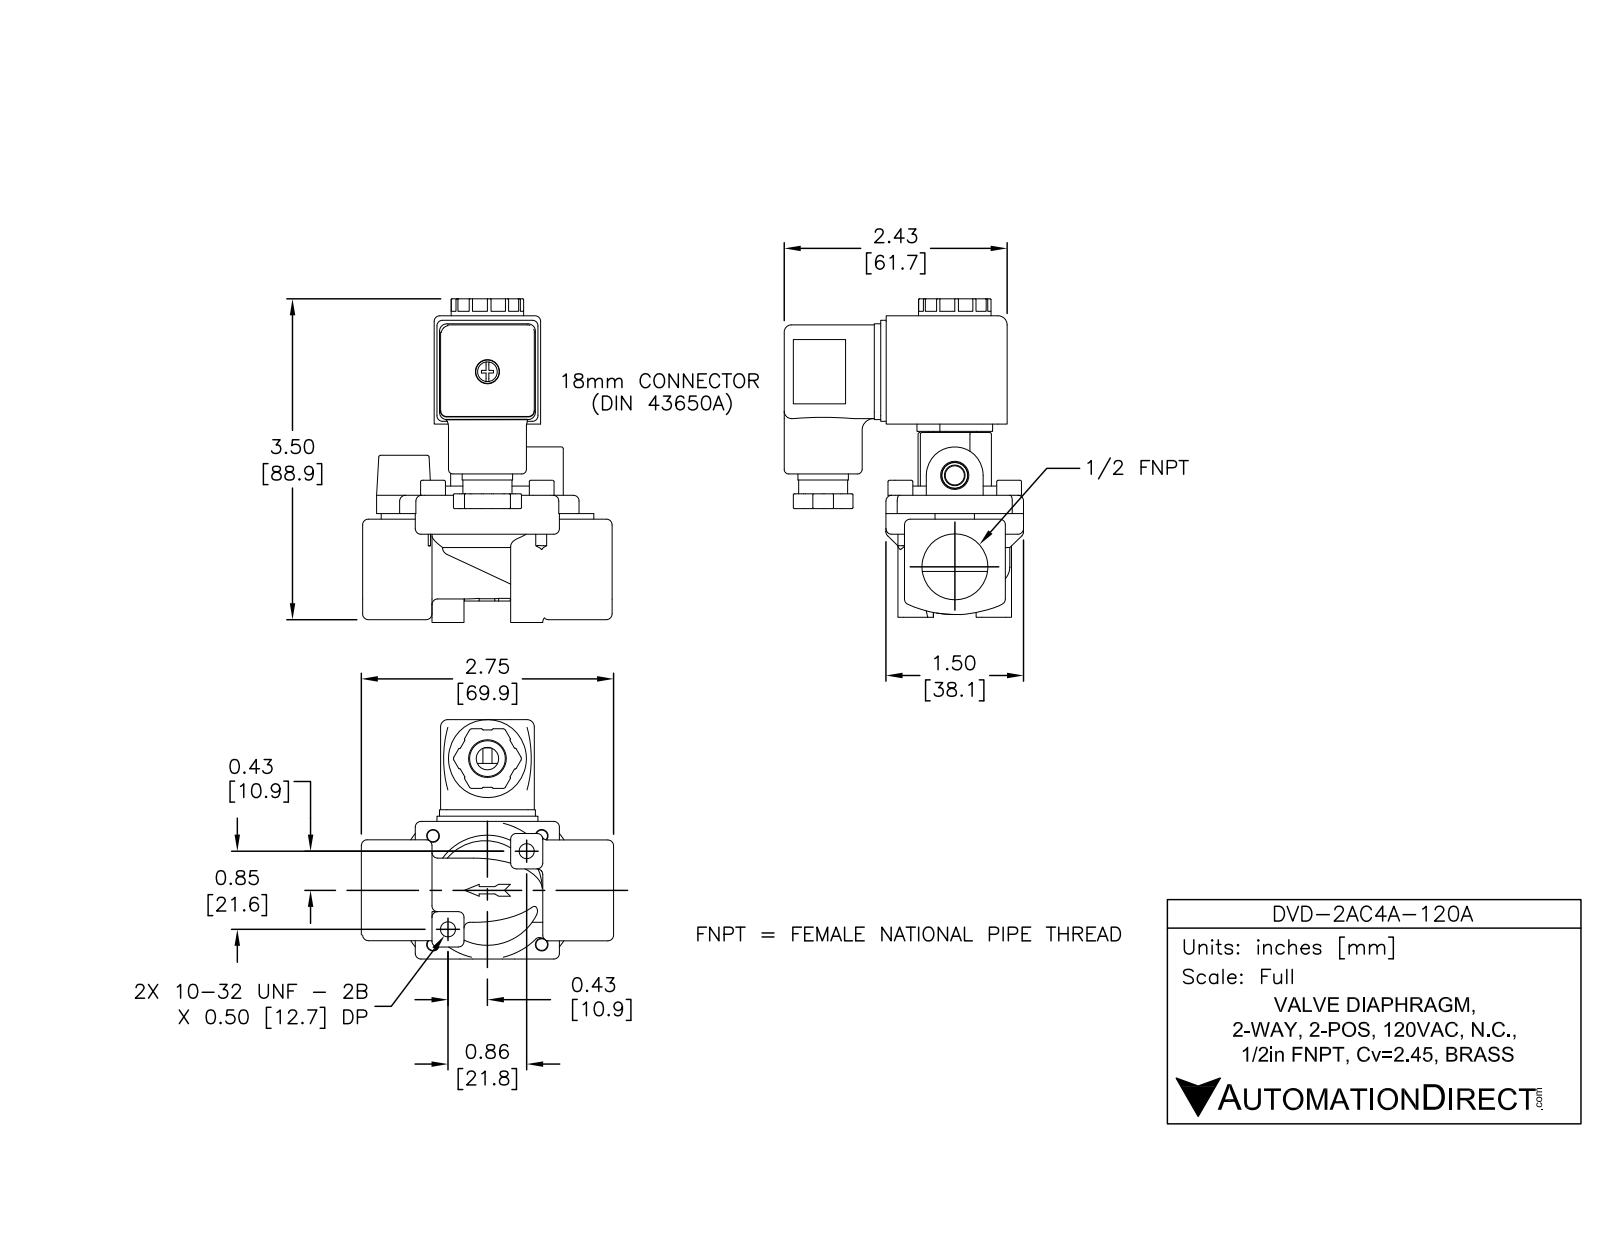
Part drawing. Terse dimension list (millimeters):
name: DVD-2AC4A-120A
written by: SolidWorks 2015 (AUTOMOTIVE_DESIGN)
unit: mm
bodies: 9 solids, 1878 faces (872 planar, 415 cylindrical, 591 other)
size: 88.2 × 69.1 × 66.3
volume: 92 240 mm³; area: 44 350 mm²
holes: 6× ⌀4.2, 4× ⌀3.5, 2× ⌀1.5, 2× ⌀2.5, 2× ⌀3.6, 2× ⌀11, 2× ⌀17.9, 1× ⌀1.6, 1× ⌀2, 1× ⌀2.3, 1× ⌀2.4, 1× ⌀2.6
bosses: 4× ⌀6.9, 4× ⌀4.5, 4× ⌀4.1, 1× ⌀34.9, 1× ⌀21.6, 1× ⌀20.1, 1× ⌀15.5, 1× ⌀15
rounds: 52× R0.3, 22× R1.6, 21× R1.6, 14× R1.6, 12× R2, 12× R4, 8× R1.3, 6× R0.8
face distances: 23.5, 5.1, 29.5, 30, 26.3, 27.9, 2, 1.5, 24.3, 33
hole spacings: 21.3, 23.5, 23.5, 30.1, 11.4, 19.8, 31.2, 5.9
